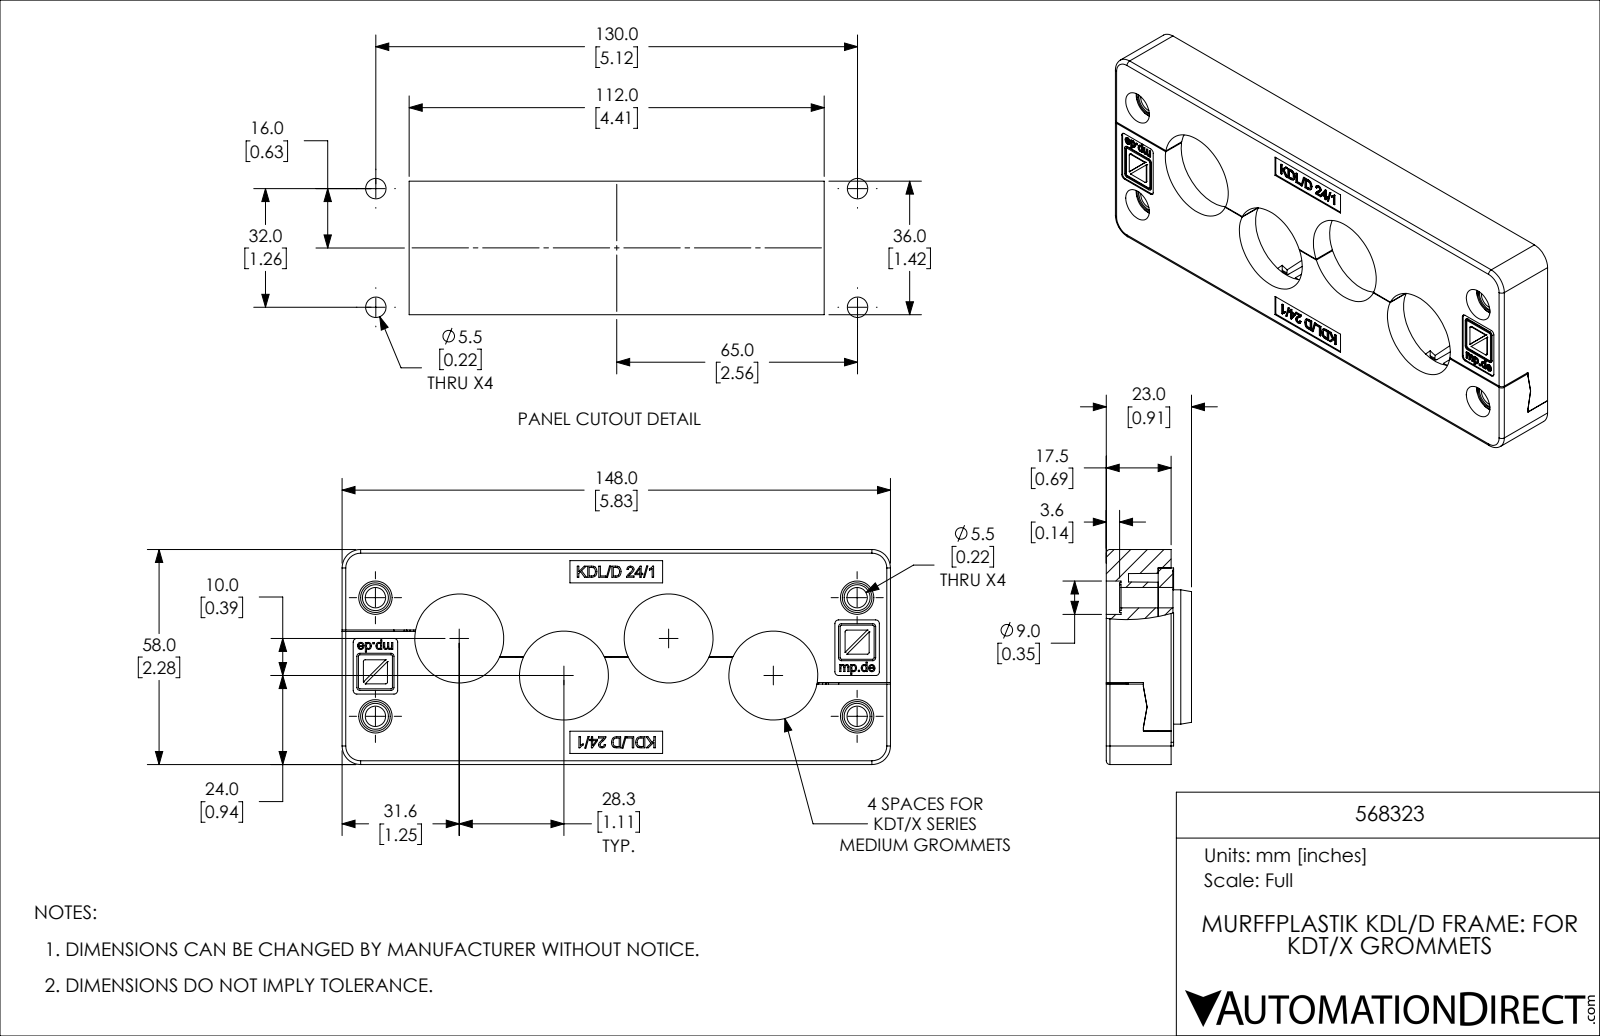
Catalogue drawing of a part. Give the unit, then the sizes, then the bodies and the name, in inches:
Units: inches
Overall size (bounding box): 5.827 × 2.283 × 0.906
Round holes (diameter × count): ⌀0.217 ×6, ⌀0.276 ×4, ⌀0.354 ×4, ⌀0.982 ×4, ⌀0.197 ×2, ⌀0.236 ×2
Round bosses / shafts (diameter × count): ⌀0.315 ×4
Partial cylindrical surfaces — rounded edges, fillets, slot ends (radius × count): R0.039 ×32, R0.02 ×19, R0.016 ×12, R0.031 ×8, R0.472 ×8, R0.004 ×4, R0.006 ×4, R0.012 ×4
Main face-to-face distances: 0.197, 2.087, 0.236, 0.157, 0.551, 0.02, 2.283, 0.709, 0.472, 0.138
Hole centre spacings: 1.18, 0.394, 0.866, 0.991, 1.215, 1.26, 2.05, 2.224
Volume: 6.956 in³ · Surface area: 82.73 in²
Bodies: 3 solids, 1136 faces (665 planar, 212 cylindrical, 259 other)
Part name (STEP PRODUCT): 568323
STEP written by: SolidWorks 2019 (CONFIG_CONTROL_DESIGN)
